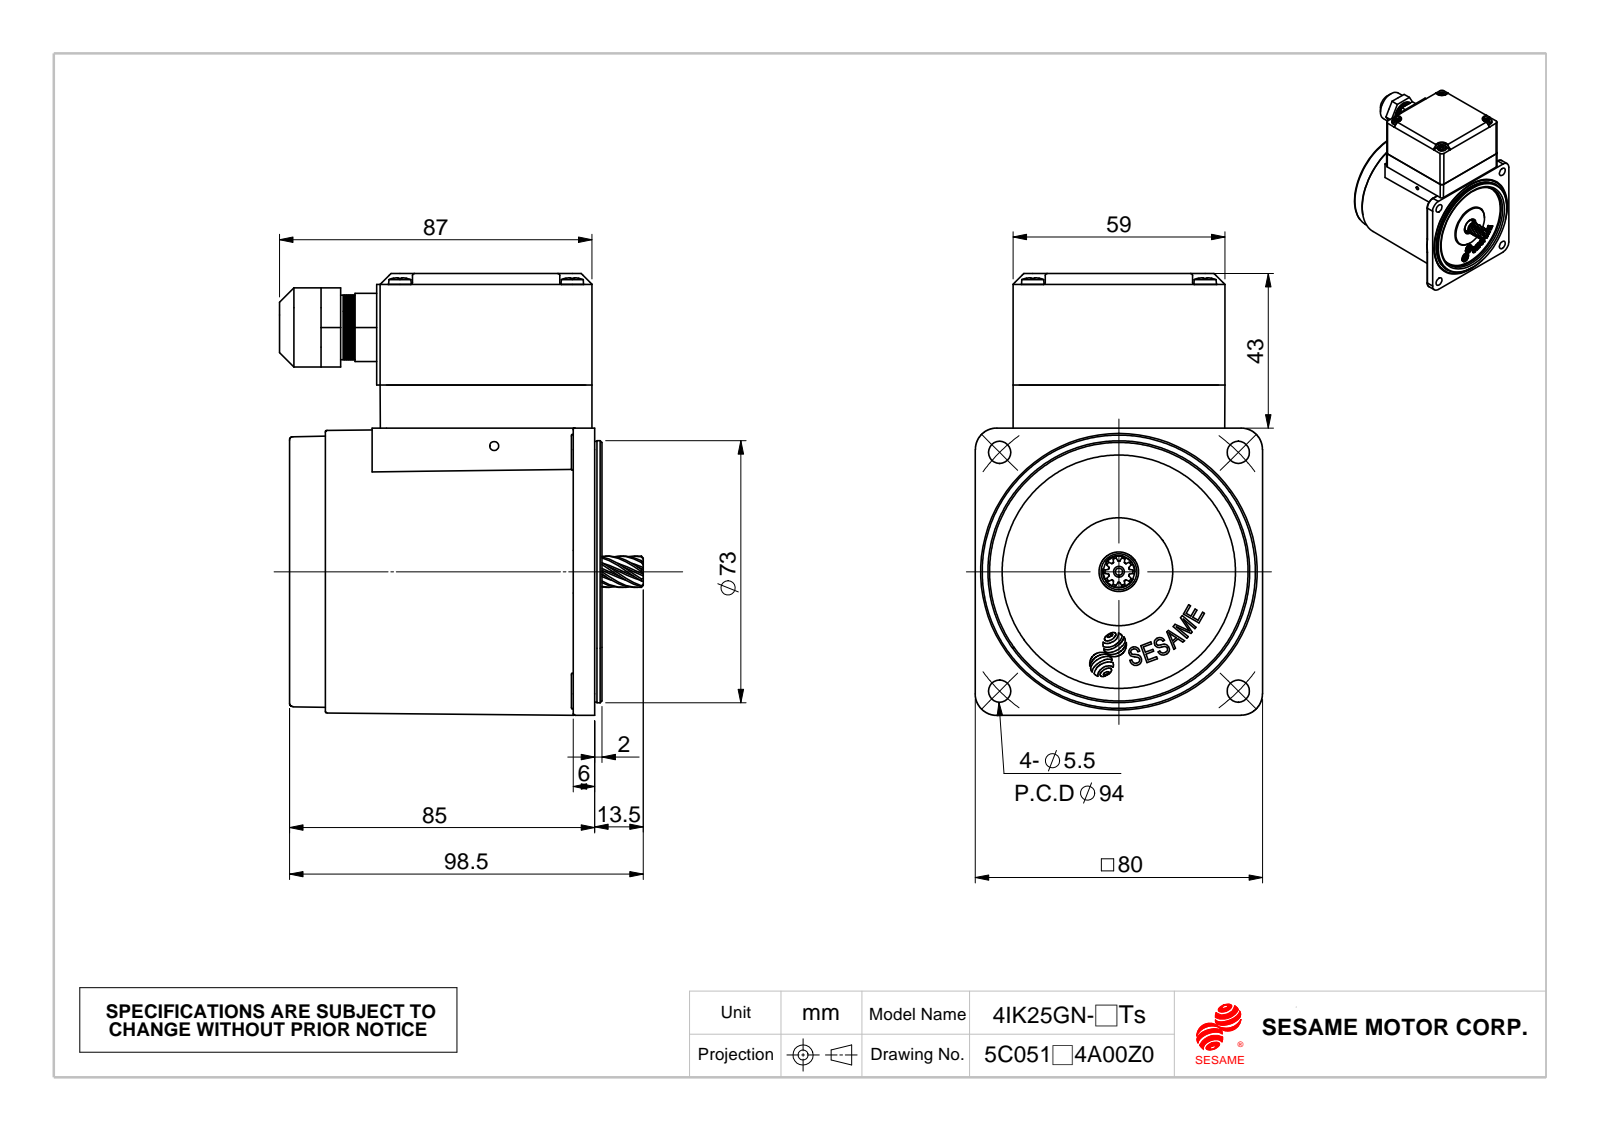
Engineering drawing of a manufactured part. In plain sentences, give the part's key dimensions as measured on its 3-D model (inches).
The part is named "成品180度; 25GN_Default; M425TsA_成品; C475-C473_C475成品-車工 (+1 more)". Its 3-D file was written by "SolidWorks 2010 (CONFIG_CONTROL_DESIGN)". It is 11 solids with 2687 faces: 281 planar, 939 cylindrical and 1467 other. Overall it measures 4.843 by 3.986 by 3.15 inches. Its volume is 15.6 cubic inches and its surface area 157 square inches. Round holes: 4 of diameter 0.13, 4 of diameter 0.138, 4 of diameter 0.154, 4 of diameter 0.169, 4 of diameter 0.244, 2 of diameter 0.433, 1 of diameter 0.079, 1 of diameter 0.098, 1 of diameter 0.472, 1 of diameter 0.571, 1 of diameter 2.362, 1 of diameter 2.559. Round bosses or shafts: 4 of diameter 0.248, 4 of diameter 0.118, 1 of diameter 2.871, 1 of diameter 2.856, 1 of diameter 1.457, 1 of diameter 0.866, 1 of diameter 0.709, 1 of diameter 0.394. Partial cylindrical surfaces (rounded edges, fillets, slot ends): 12 of radius 0.02, 12 of radius 0.079, 8 of radius 0.024, 8 of radius 0.046, 8 of radius 0.051, 8 of radius 0.089, 6 of radius 0.157, 4 of radius 0.006. The main face-to-face distances are 0.472, 0.039, 0.059, 0.02, 0.118, 0.03, 3.307, 3.15, 3.268, 3.248. The hole center spacings are 1.85, 1.89, 2.617, 0.459, 0.486, 0.5, 0.981, 0.984.
